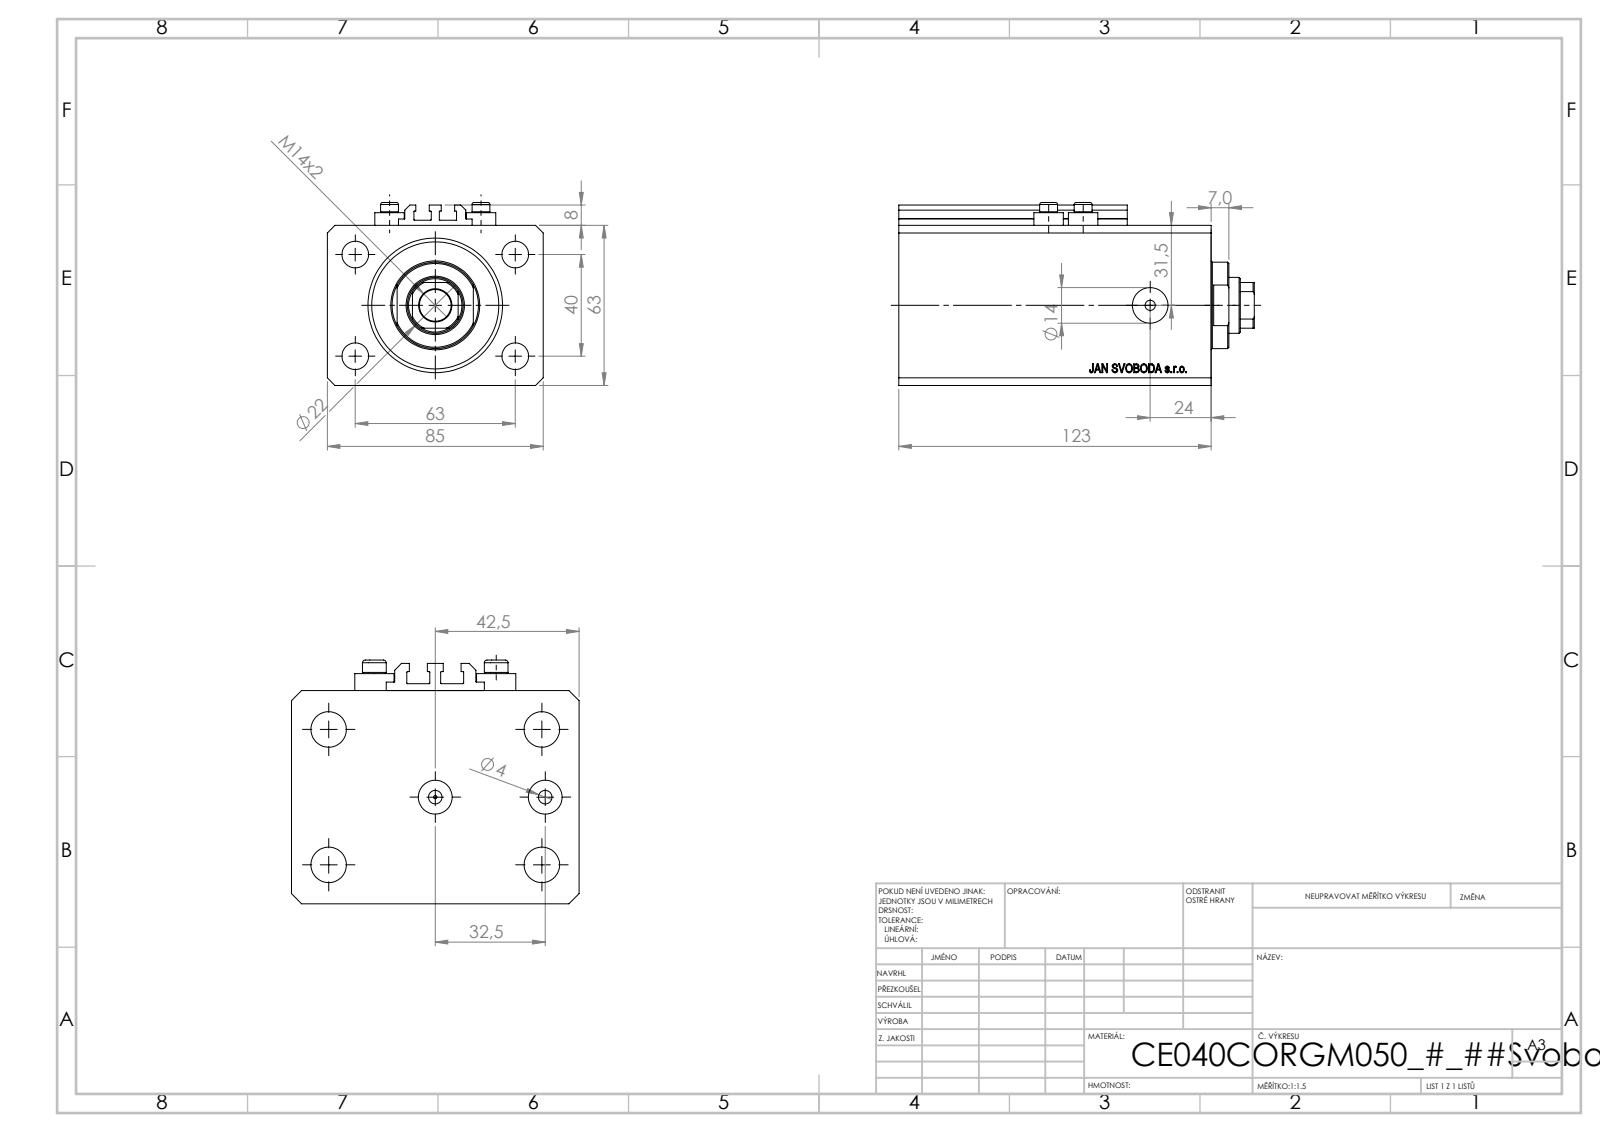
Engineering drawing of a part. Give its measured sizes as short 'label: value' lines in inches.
name: V250CE_C_Body; V250CE_C_VCP; V250CE_VC_C; ALLEN BOLT V250CE
written by: SolidWorks 2019 (CONFIG_CONTROL_DESIGN)
unit: in
bodies: 8 solids, 1038 faces (504 planar, 88 cylindrical, 446 other)
size: 5.512 × 3.346 × 2.835
volume: 35.81 in³; area: 177 in²
holes: 8× ⌀0.157, 4× ⌀0.413, 2× ⌀0.394, 2× ⌀0.551, 1× ⌀0.049, 1× ⌀0.492, 1× ⌀0.866, 1× ⌀1.575, 1× ⌀2.087
bosses: 4× ⌀0.457, 4× ⌀0.276, 1× ⌀1.339
rounds: 10× R0.008, 1× R0.413
face distances: 2.48, 3.346, 4.843, 0.669, 4.173, 0.449, 3.724, 4.394, 0.098, 0.394
hole spacings: 1.469, 0.535, 0.788, 1.417, 1.515, 1.575, 2.48, 2.64
